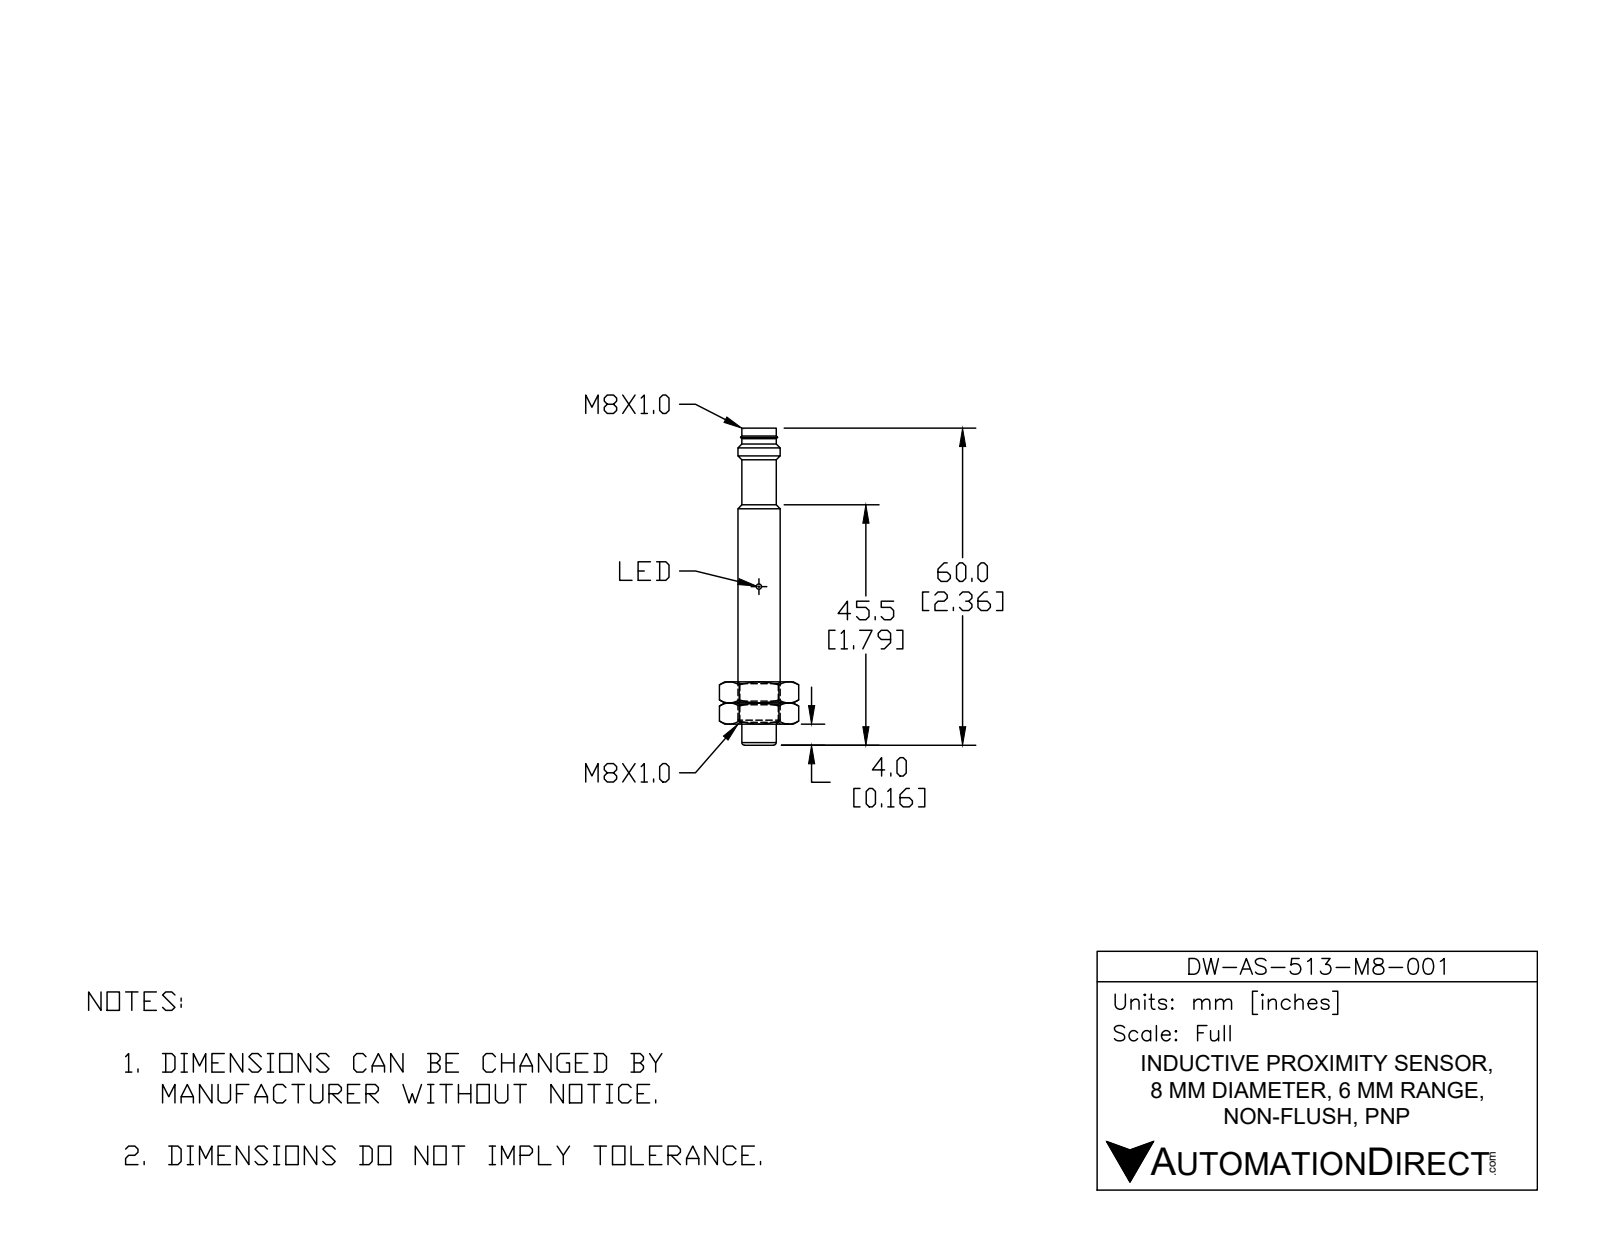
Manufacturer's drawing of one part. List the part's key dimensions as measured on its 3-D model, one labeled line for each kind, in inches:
Part name (STEP PRODUCT): DW-AS-513-M8-001
STEP written by: SolidWorks 2017 (AUTOMOTIVE_DESIGN)
Units: inches
Bodies: 1 solid, 33 faces (3 planar, 18 cylindrical, 12 other)
Overall size (bounding box): 2.362 × 0.315 × 0.315
Volume: 0.16 in³ · Surface area: 2.606 in²
Round holes (diameter × count): ⌀0.071 ×2
Round bosses / shafts (diameter × count): ⌀0.039 ×3, ⌀0.315 ×1, ⌀0.272 ×1, ⌀0.256 ×1, ⌀0.236 ×1
Main face-to-face distances: 2.165, 2.362, 0.197
